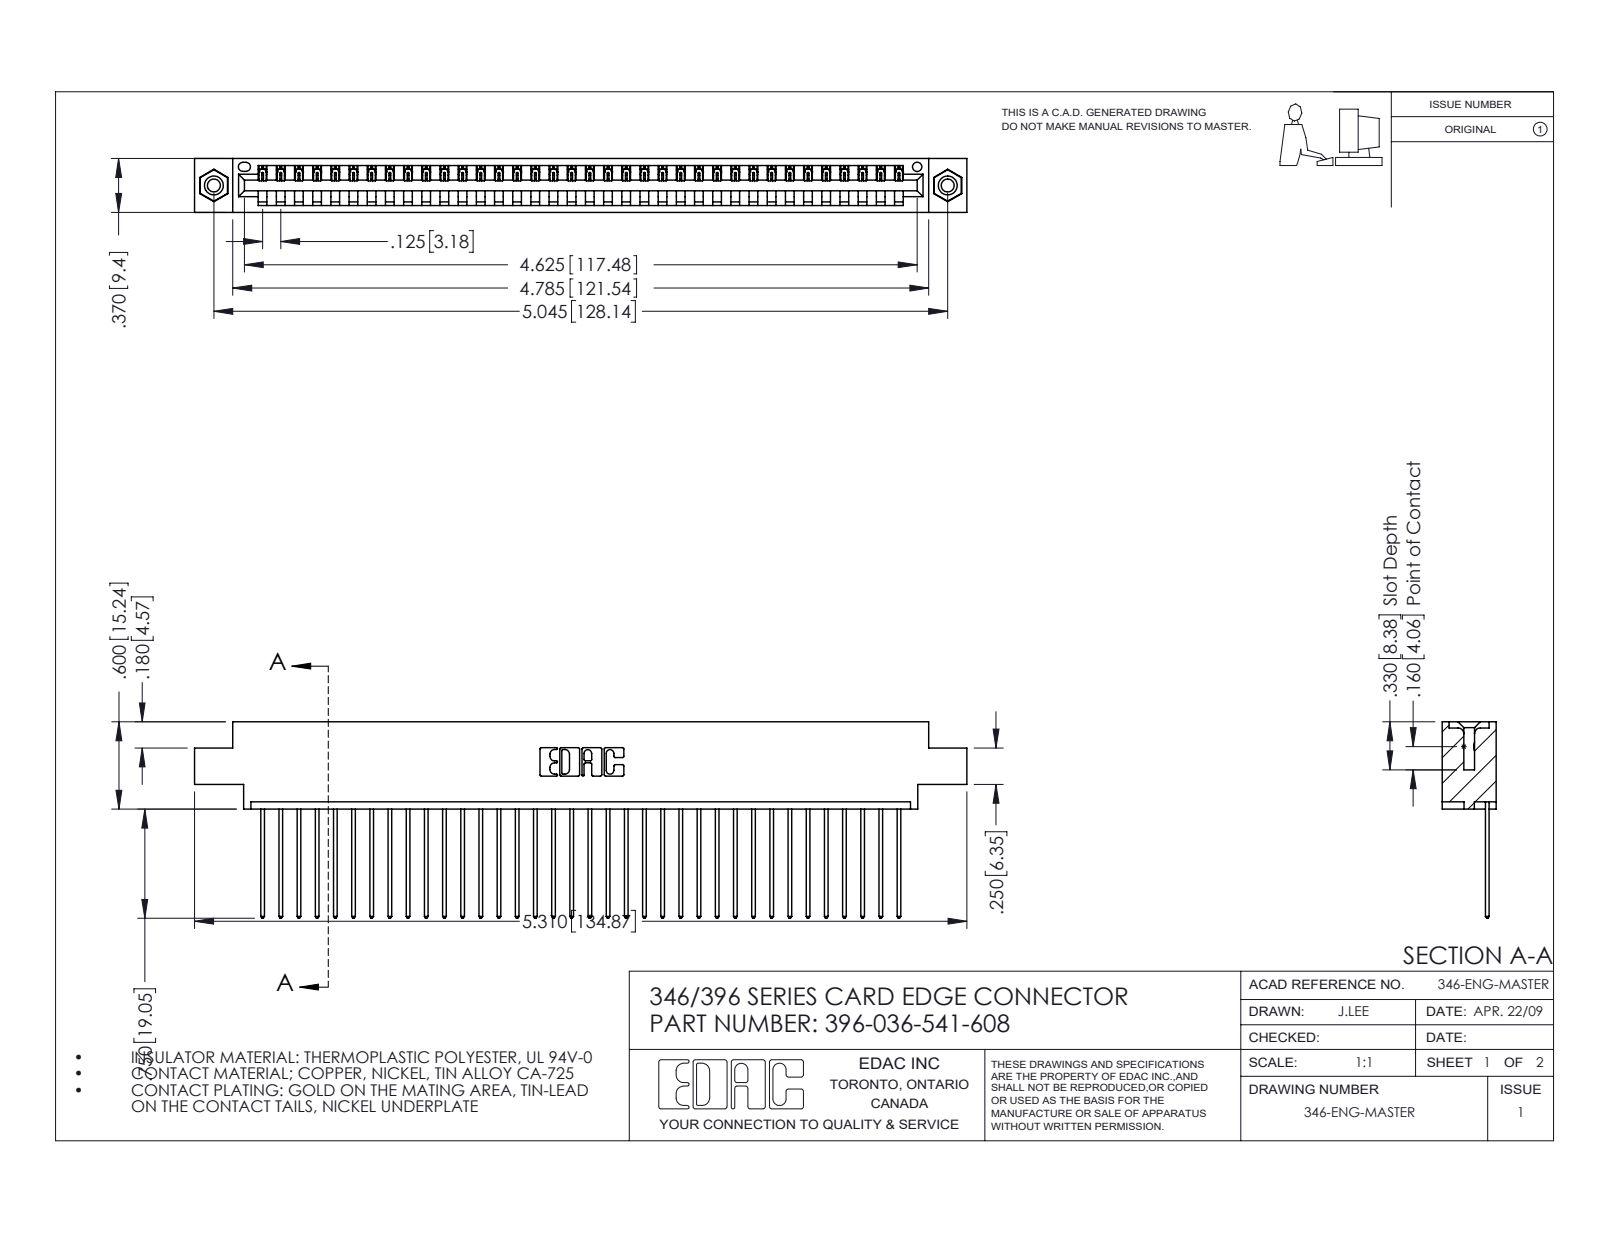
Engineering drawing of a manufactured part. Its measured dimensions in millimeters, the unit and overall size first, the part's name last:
Units: millimetres
Overall size (bounding box): 134.9 × 34.3 × 9.4
Round holes (diameter × count): ⌀2.3 ×2, ⌀3.2 ×2, ⌀4 ×2, ⌀1.6 ×1
Round bosses / shafts (diameter × count): ⌀3.9 ×2
Partial cylindrical surfaces — rounded edges, fillets, slot ends (radius × count): R0.2 ×72, R0.3 ×72, R0.3 ×22, R0.2 ×6, R0.8 ×6, R0.7 ×3, R0.8 ×2, R1 ×2
Main face-to-face distances: 1.2, 8.2, 9.4, 6.4, 1.8, 7.6, 0.6, 5.6, 3.8, 2.5
Hole centre spacings: 6.2, 122.8, 128.1
Volume: 12 800 mm³ · Surface area: 16 860 mm²
Bodies: 39 solids, 2274 faces (1552 planar, 706 cylindrical, 16 other)
Part name (STEP PRODUCT): 345-292-001_345-293-141; 346 Part_0.170 Offset - 0.156 Dia-TI; 396-036-541-608; 345-250-001_345-250-003-102
STEP written by: SolidWorks 2016 (CONFIG_CONTROL_DESIGN)
